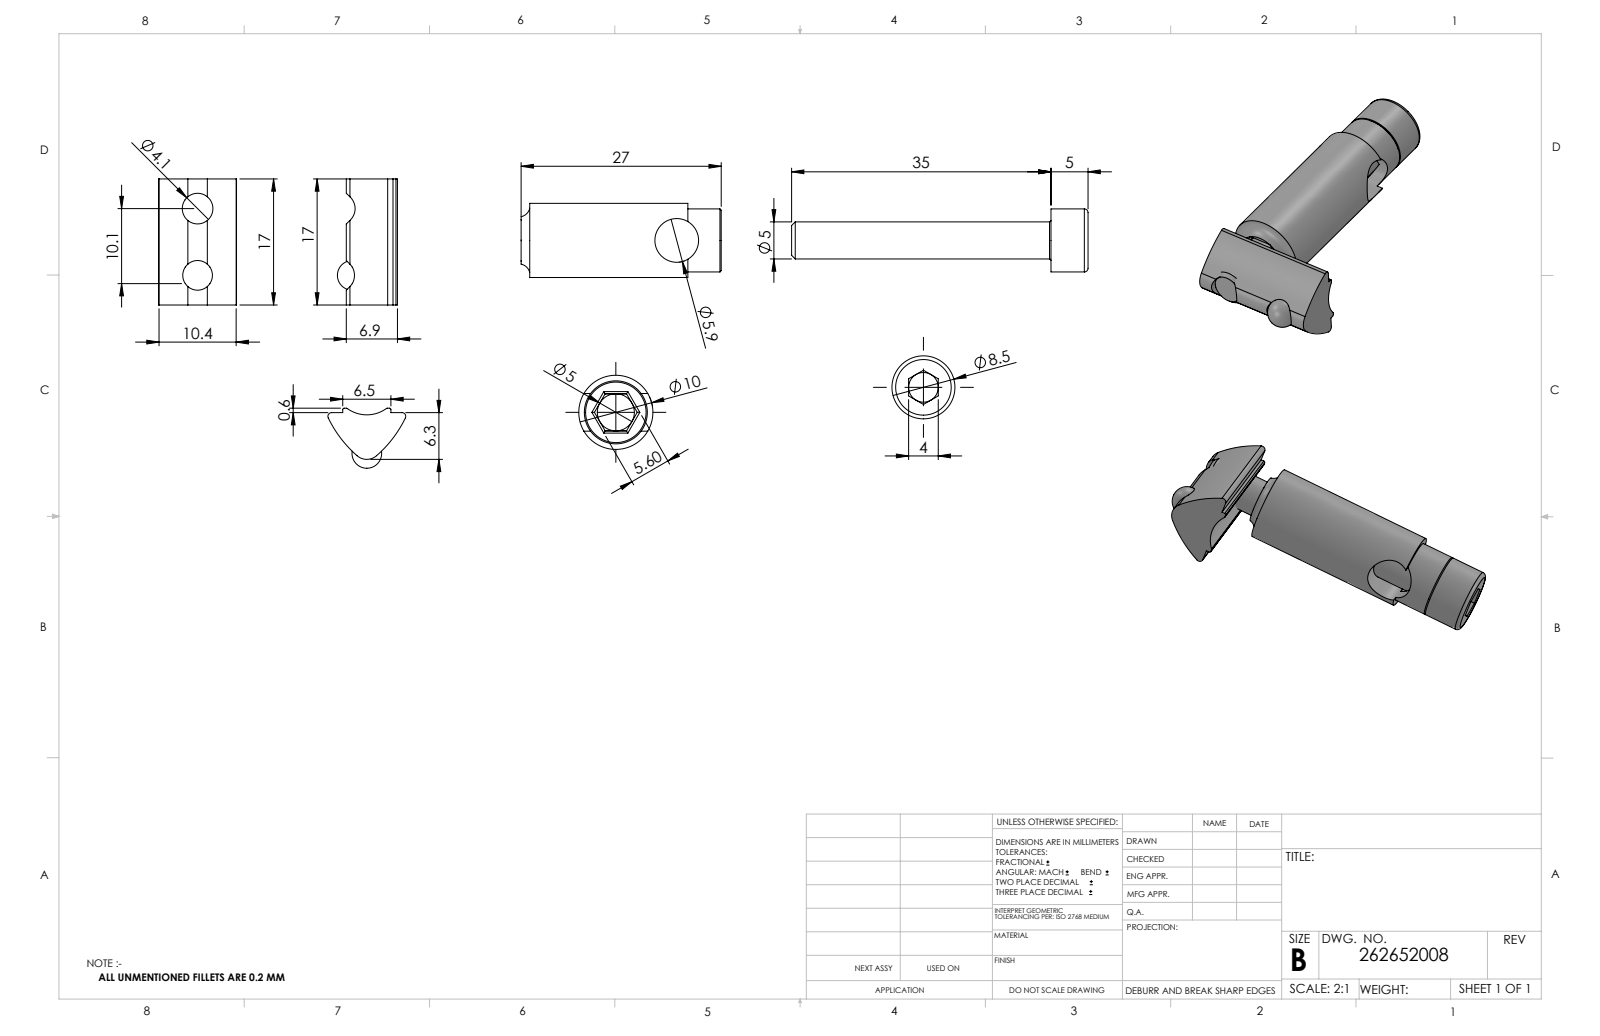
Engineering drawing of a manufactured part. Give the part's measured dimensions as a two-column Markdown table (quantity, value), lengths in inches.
| quantity | value |
| --- | --- |
| part name | 262652008_Automatikverbinder_Nut6_Shrinkwrap_1 |
| STEP written by | Autodesk Inventor 2019 (AUTOMOTIVE_DESIGN) |
| units | inches |
| bodies | 3 solids, 96 faces (66 planar, 23 cylindrical, 7 other) |
| overall size | 1.654 × 0.709 × 0.414 |
| volume | 0.177 in³ |
| surface area | 4.314 in² |
| round holes (diameter × count) | 0.163 × 1, 0.197 × 1, 0.232 × 1 |
| round bosses / shafts (diameter × count) | 0.394 × 1, 0.335 × 1 |
| partial cylindrical surfaces (radius × count) | 0.008 × 4, 0.02 × 2, 0.079 × 2, 0.63 × 2, 0.177 × 1 |
| main face-to-face distances | 0.197, 1.161, 0.669, 1.358, 0.157, 0.984, 0.177, 0.374, 0.03, 0.226 |
